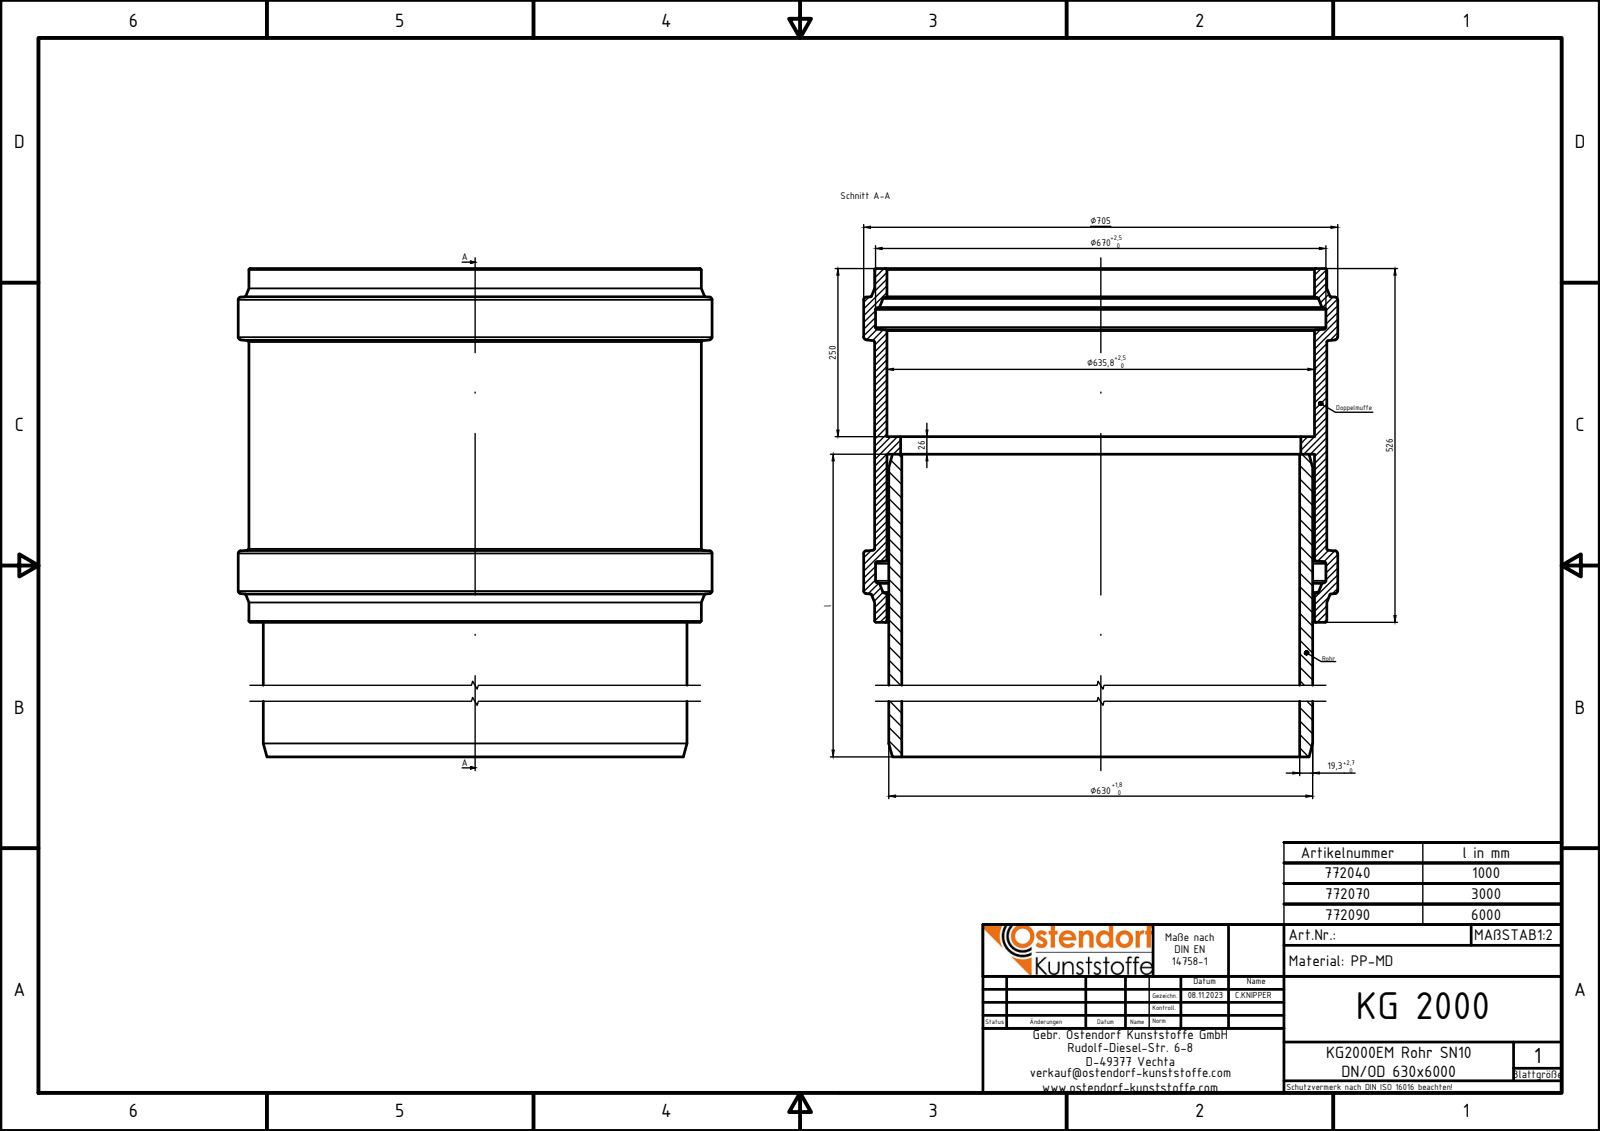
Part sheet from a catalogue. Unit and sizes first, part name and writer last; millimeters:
Units: millimetres
Overall size (bounding box): 6276 × 704.8 × 704.8
Round holes (diameter × count): ⌀591.4 ×1, ⌀594.8 ×1, ⌀635.8 ×1, ⌀670 ×1
Round bosses / shafts (diameter × count): ⌀704.8 ×1, ⌀672.6 ×1, ⌀630 ×1
Main face-to-face distances: 276, 250, 526, 5750, 6026, 6276, 6000, 26
Volume: 244 700 000 mm³ · Surface area: 25 550 000 mm²
Bodies: 1 solid, 60 faces (6 planar, 14 cylindrical, 40 other)
Part name (STEP PRODUCT): 772090z
STEP written by: Autodesk Inventor 2024 (AUTOMOTIVE_DESIGN)
